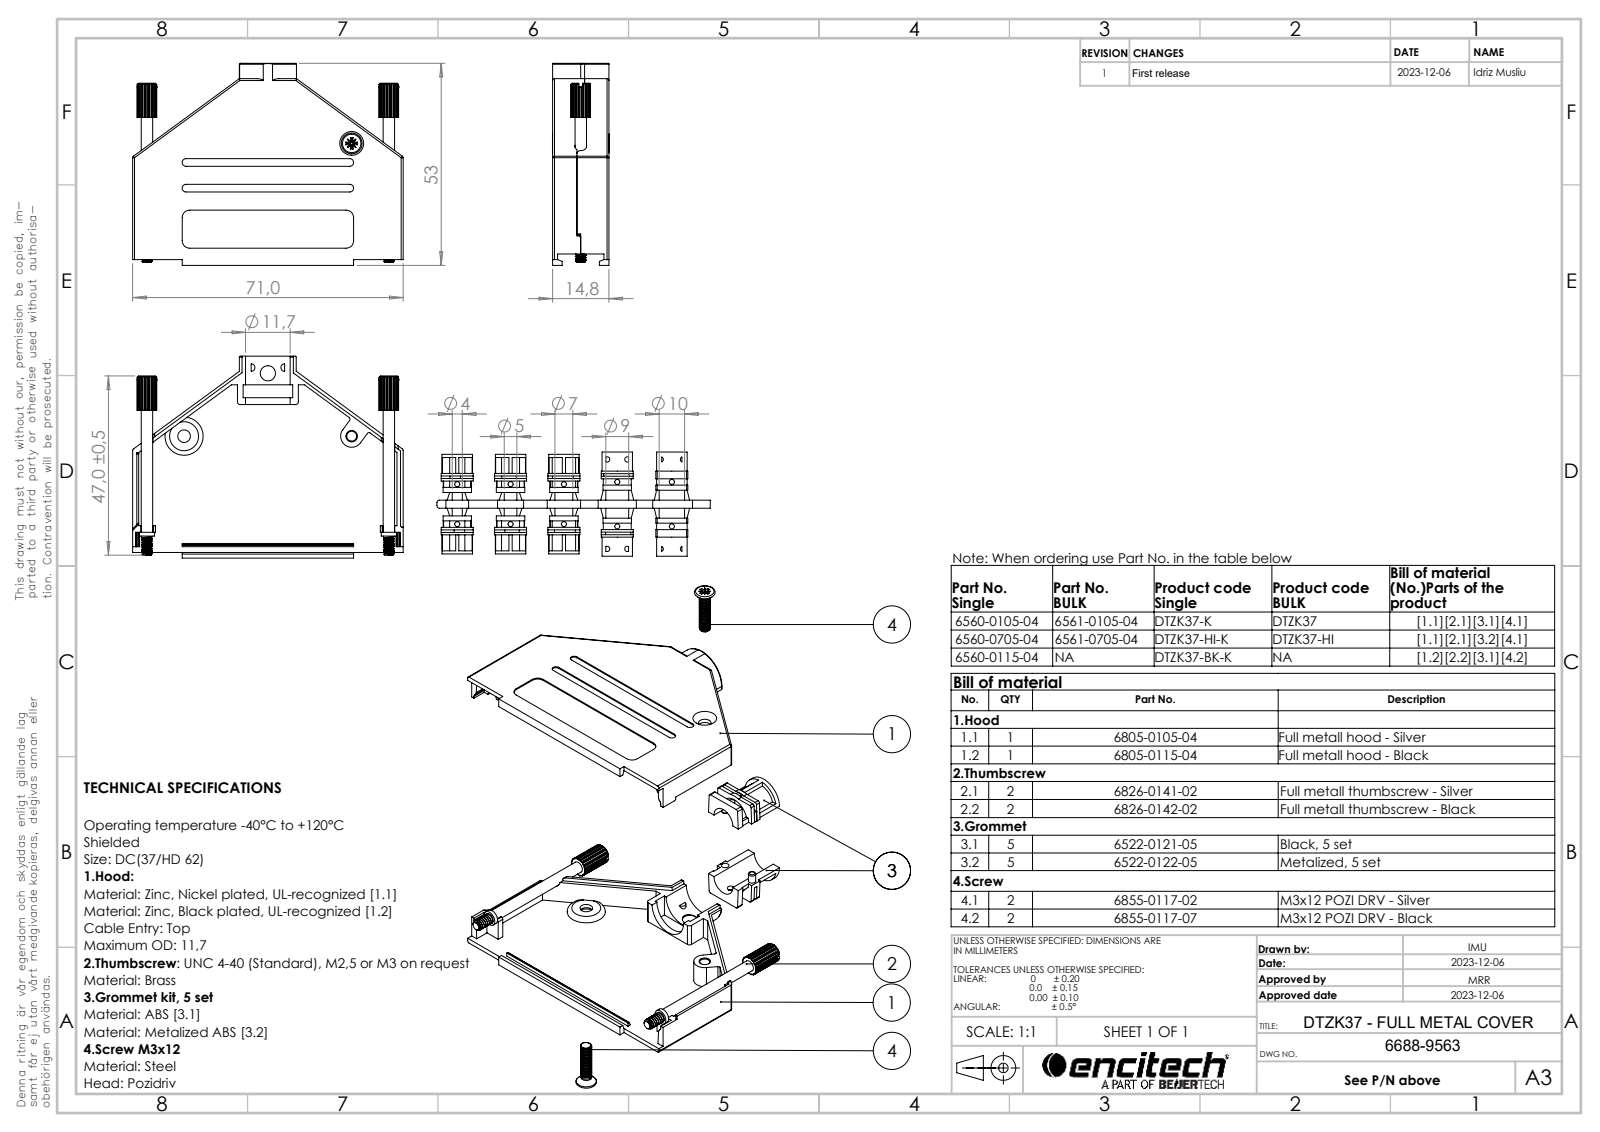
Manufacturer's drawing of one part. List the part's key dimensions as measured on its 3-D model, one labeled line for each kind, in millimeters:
Part name (STEP PRODUCT): 6805-0105-04; 6826-0141-02; 6855-0117-02; 6522-0121-05 (7mm) (+1 more)
STEP written by: SolidWorks 2021 (AUTOMOTIVE_DESIGN)
Units: millimetres
Bodies: 8 solids, 834 faces (446 planar, 310 cylindrical, 78 other)
Overall size (bounding box): 71 × 53 × 14.85
Volume: 12 759 mm³ · Surface area: 20 090 mm²
Round holes (diameter × count): ⌀2 ×3, ⌀2.6 ×2, ⌀3.1 ×2, ⌀3.3 ×2, ⌀4 ×1, ⌀7 ×1, ⌀11.7 ×1
Round bosses / shafts (diameter × count): ⌀4 ×2, ⌀3 ×2, ⌀2.9 ×2, ⌀2.85 ×2, ⌀1.9 ×2, ⌀15 ×1, ⌀11.6 ×1, ⌀9.2 ×1
Partial cylindrical surfaces — rounded edges, fillets, slot ends (radius × count): R0.5 ×32, R1 ×12, R0.1 ×8, R0.25 ×8, R2 ×4, R5.91 ×4, R0.2 ×2, R0.3 ×2
Main face-to-face distances: 1.3, 13.5, 12.2, 14.8, 1, 14.5, 13.2, 6.1, 1.6, 7.1
Hole centre spacings: 5.71, 6.97, 20.61, 23.73, 27.5, 29.41, 31.75, 7.6
